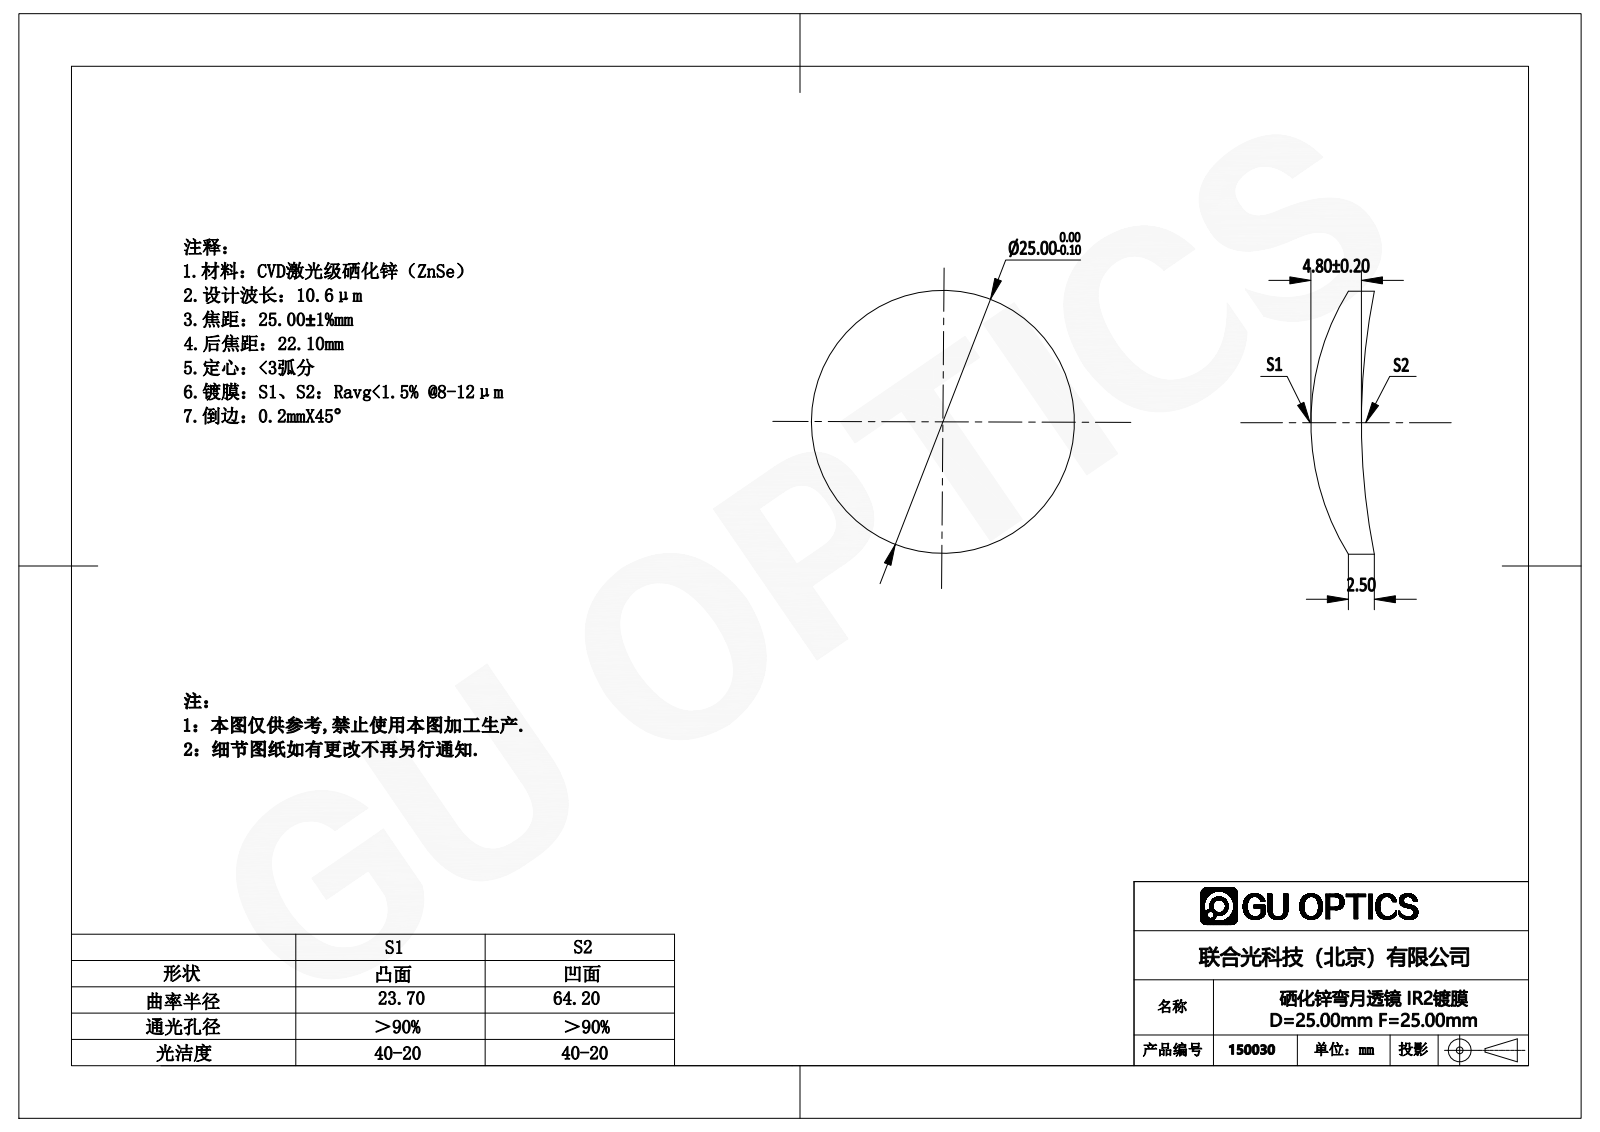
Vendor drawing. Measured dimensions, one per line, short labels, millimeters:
name: 150005
written by: SolidWorks 2016 (AUTOMOTIVE_DESIGN)
unit: mm
bodies: 1 solid, 6 faces (0 planar, 2 cylindrical, 4 other)
size: 25 × 25 × 6.03
volume: 1 806 mm³; area: 1 220 mm²
bosses: 1× ⌀25
